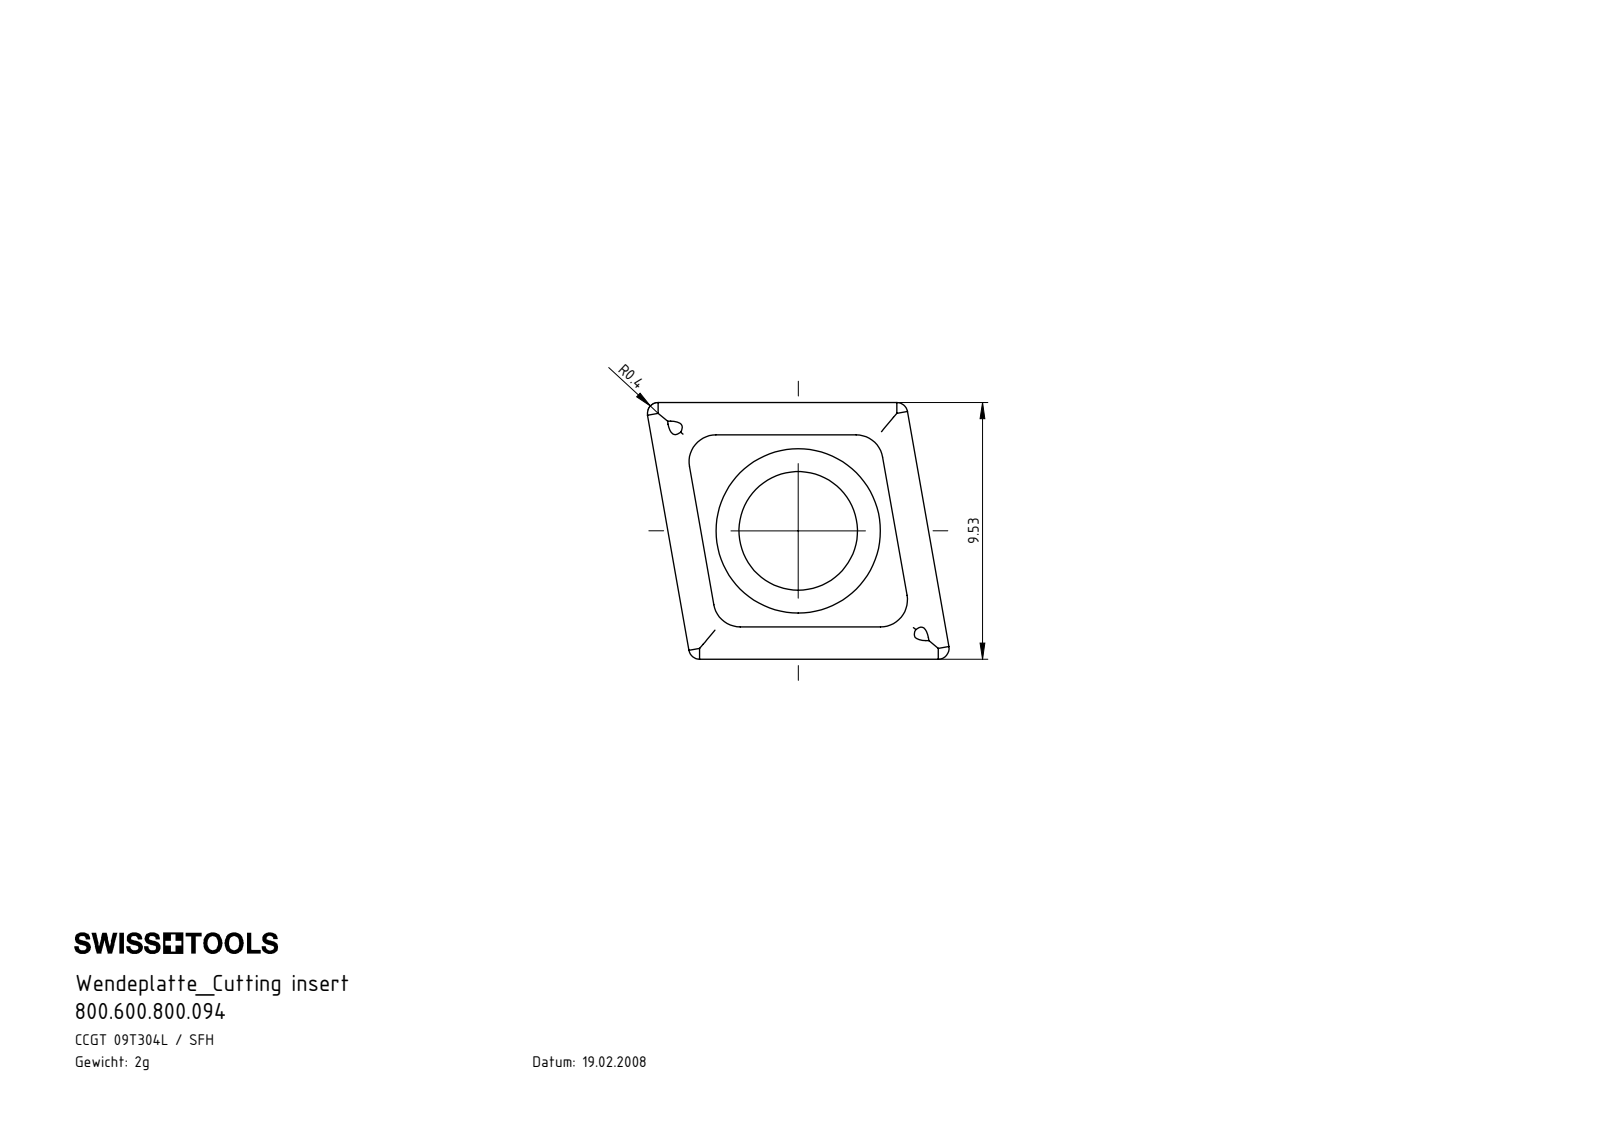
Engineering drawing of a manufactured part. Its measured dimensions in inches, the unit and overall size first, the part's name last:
Units: inches
Overall size (bounding box): 0.292 × 0.25 × 0.094
Round holes (diameter × count): ⌀0.11 ×1, ⌀0.152 ×1
Main face-to-face distances: 0.094, 0.109
Volume: 0.004 in³ · Surface area: 0.22 in²
Bodies: 1 solid, 46 faces (14 planar, 4 cylindrical, 28 other)
Part name (STEP PRODUCT): CCMT060204
STEP written by: SolidWorks 2015 (CONFIG_CONTROL_DESIGN)
